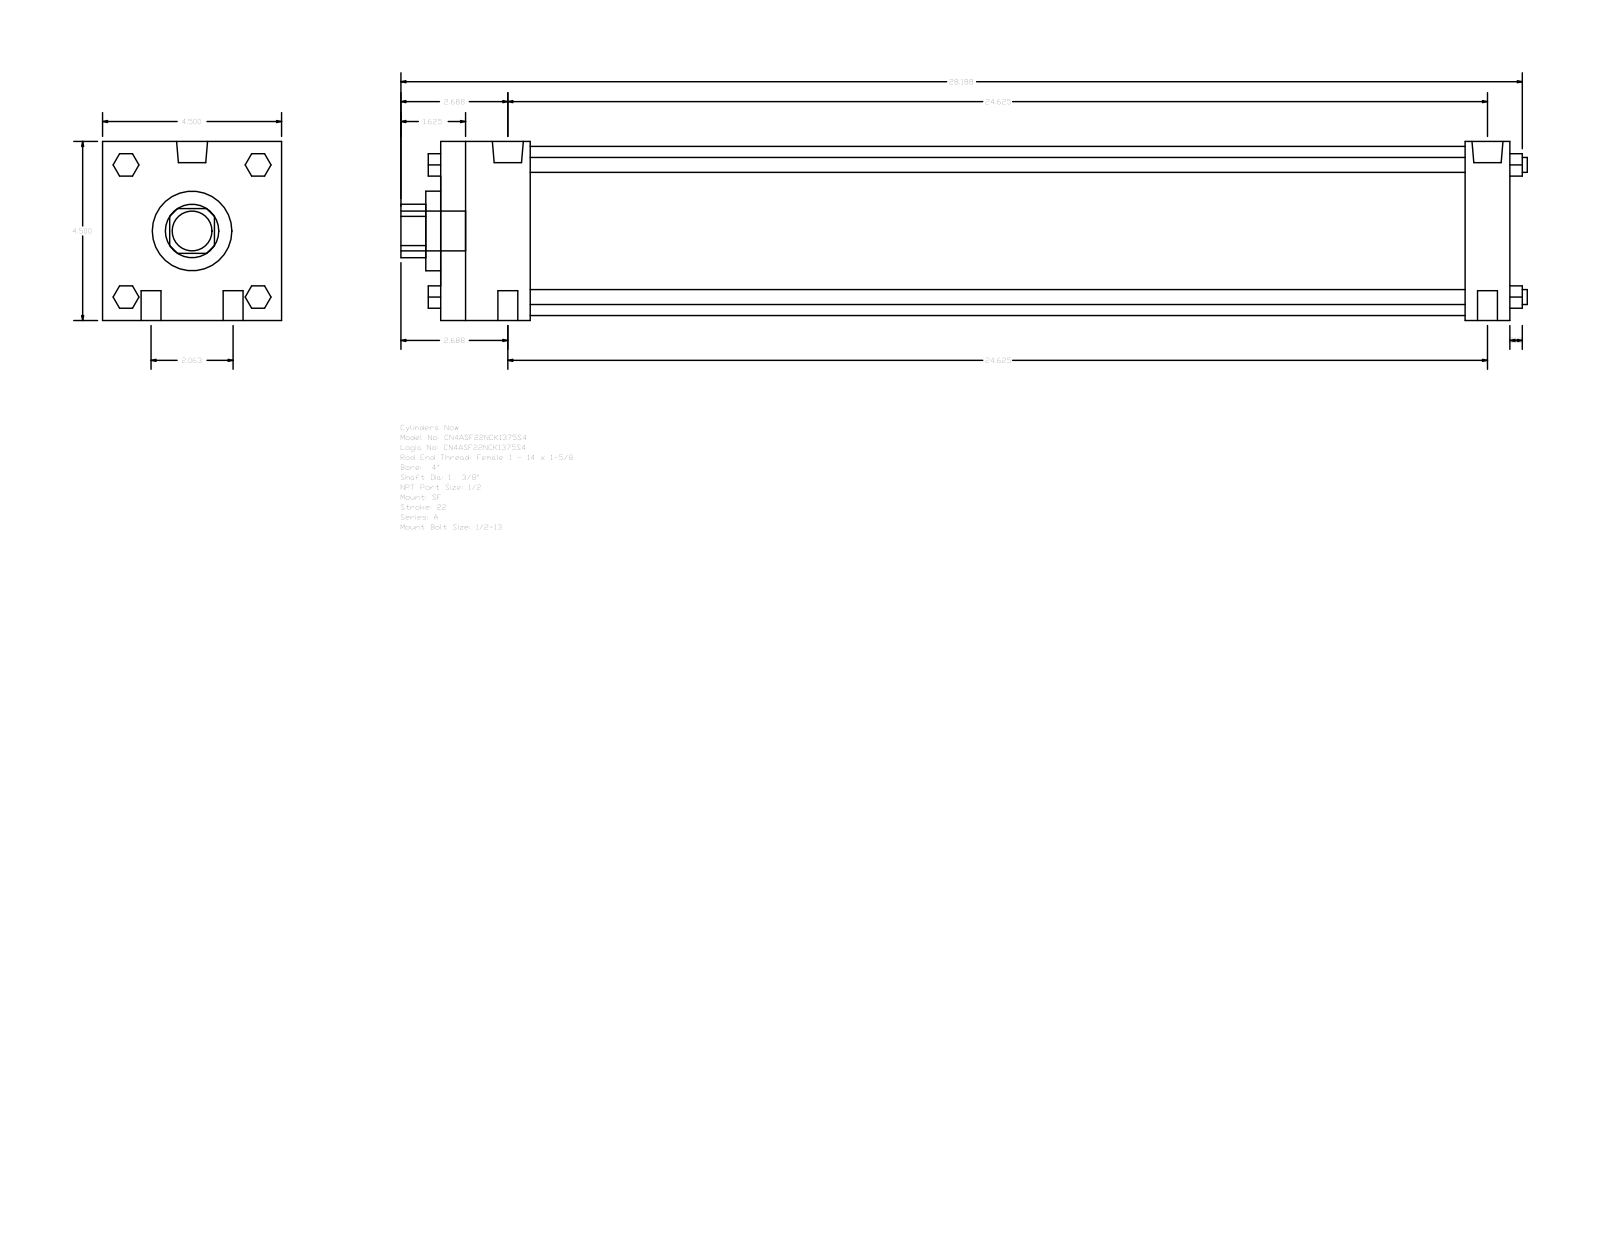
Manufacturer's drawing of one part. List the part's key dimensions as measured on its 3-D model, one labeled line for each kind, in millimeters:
Part name (STEP PRODUCT): A_SF__0400_1.375
STEP written by: GSSL Pune (CONFIG_CONTROL_DESIGN)
Units: millimetres
Bodies: 0 solids, 124 faces (94 planar, 30 cylindrical, 0 other)
Overall size (bounding box): 719.14 × 114.3 × 114.3
Round holes (diameter × count): ⌀34.92 ×1, ⌀50.8 ×1, ⌀107.95 ×1
Round bosses / shafts (diameter × count): ⌀12.7 ×4, ⌀9.53 ×4, ⌀19.77 ×2, ⌀8.73 ×2, ⌀25.4 ×1
Partial cylindrical surfaces — rounded edges, fillets, slot ends (radius × count): R17.06 ×1
Main face-to-face distances: 114.3, 682.62, 28.57, 654.05, 57.15, 596.9, 625.47, 14.29, 9.52, 66.67
